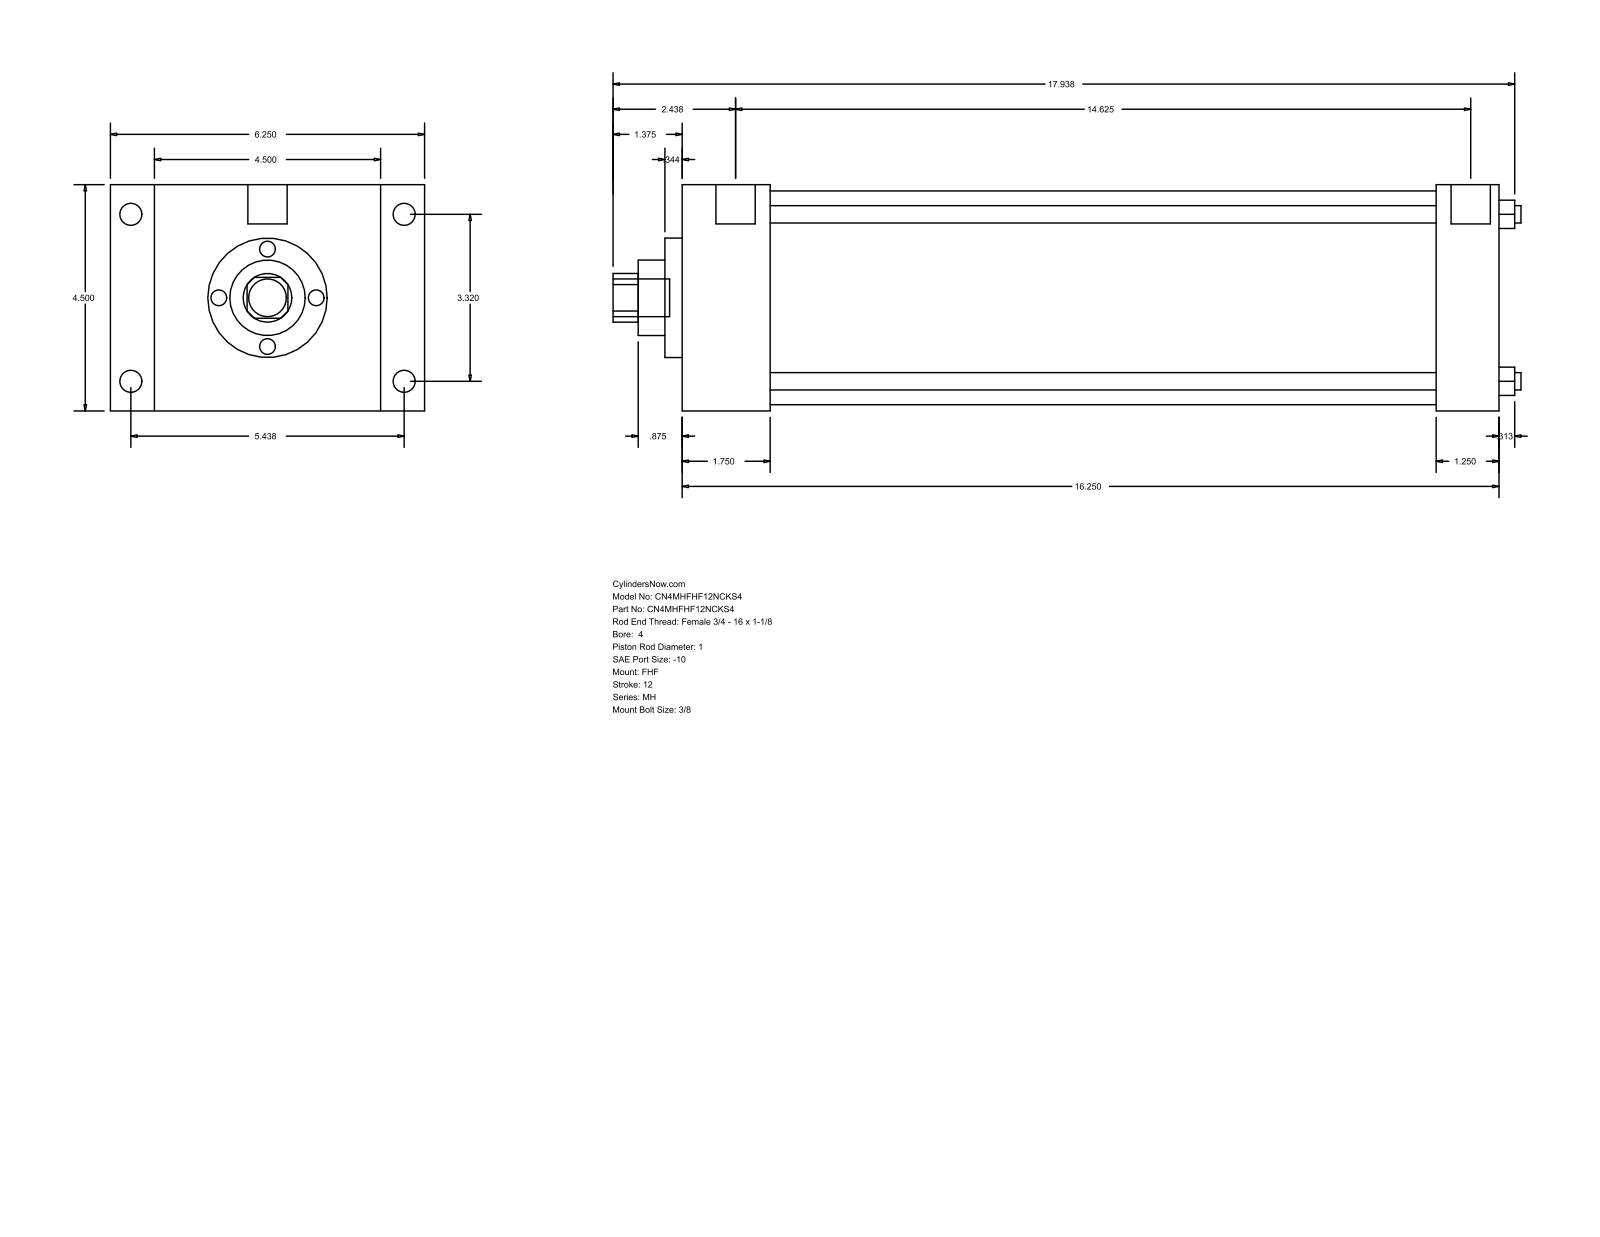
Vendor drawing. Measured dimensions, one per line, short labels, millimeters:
name: MH_FHF__0400_1
written by: GSSL Pune (CONFIG_CONTROL_DESIGN)
unit: mm
bodies: 0 solids, 90 faces (61 planar, 29 cylindrical, 0 other)
size: 458.79 × 158.75 × 114.3
holes: 4× ⌀8.76, 1× ⌀25.4, 1× ⌀38.1, 1× ⌀60.33, 1× ⌀107.95
bosses: 4× ⌀11.13, 4× ⌀8.73, 2× ⌀19.84, 1× ⌀19.05
rounds: 1× R12.29
face distances: 114.3, 412.76, 44.46, 368.3, 22.23, 136.53, 158.76, 381.01, 336.55, 31.75
hole spacings: 59.62, 84.32, 119.25
